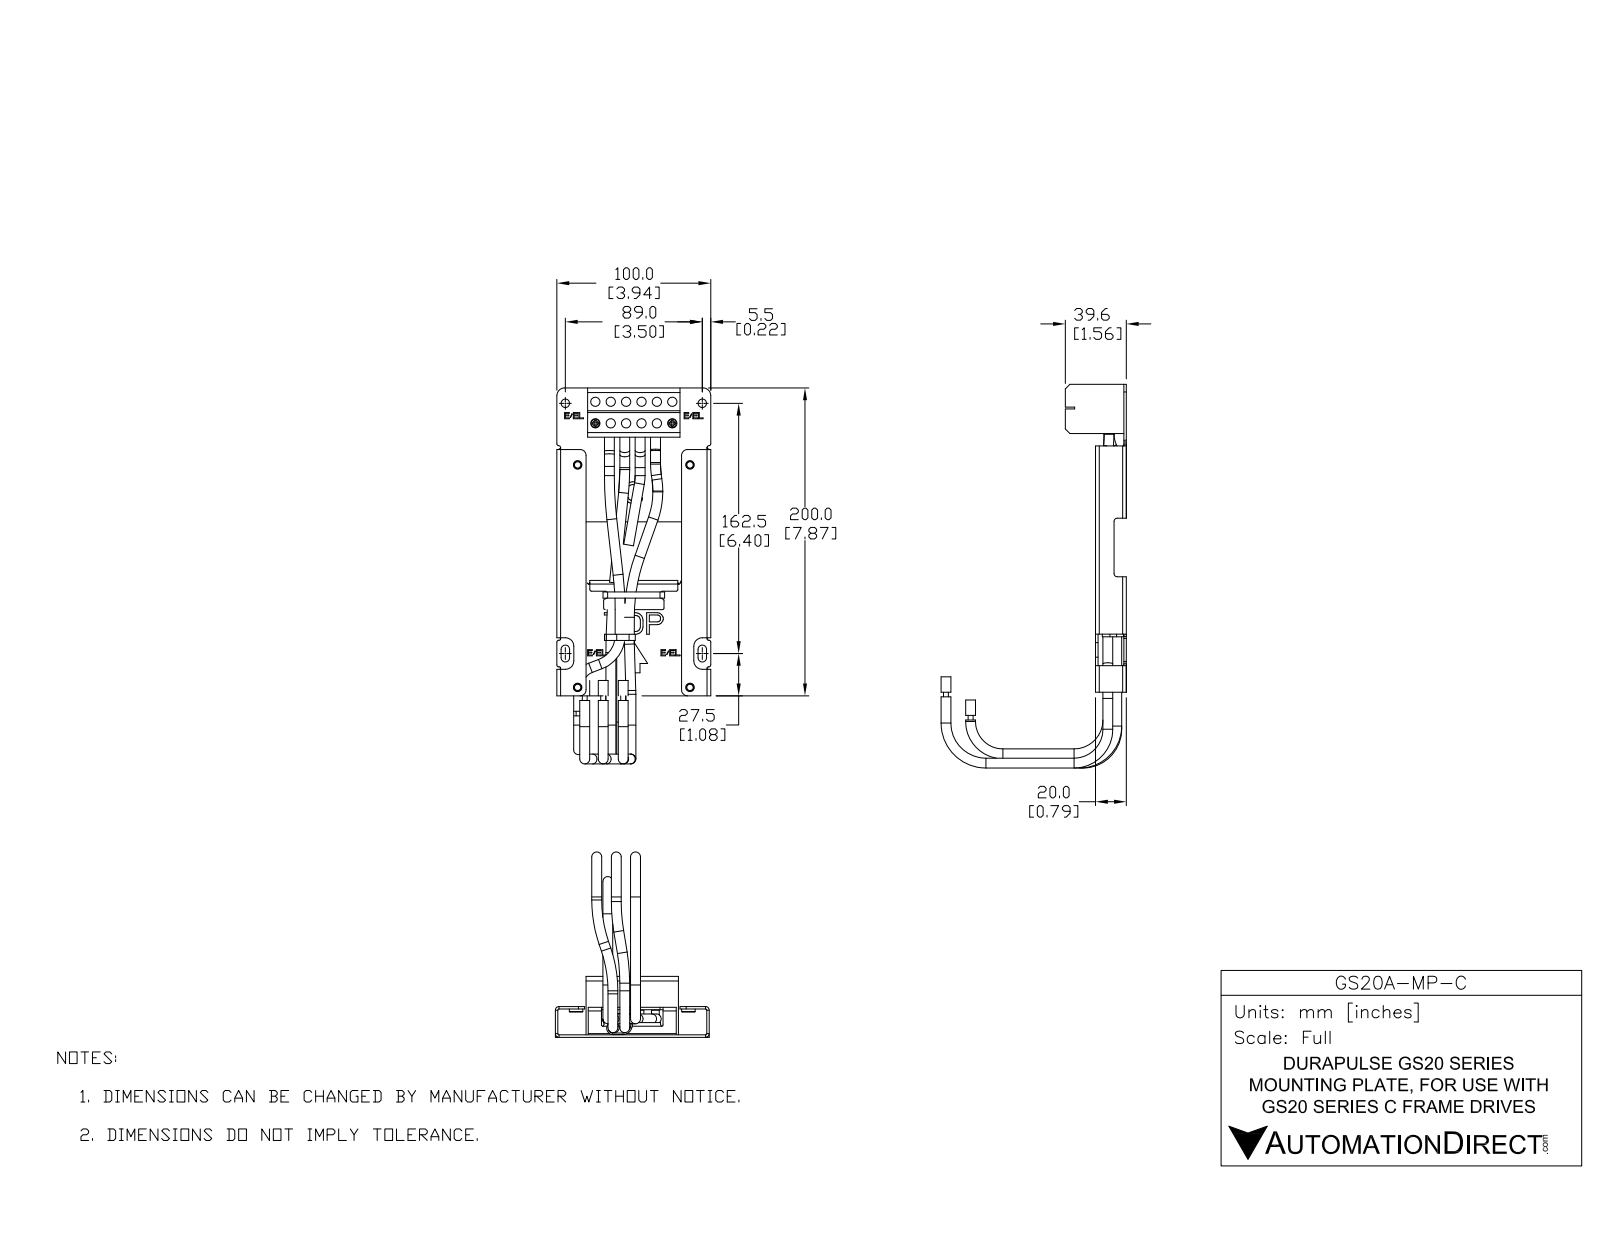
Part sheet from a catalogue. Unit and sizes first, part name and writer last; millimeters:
Units: millimetres
Overall size (bounding box): 244.2 × 117.4 × 100
Round holes (diameter × count): ⌀6 ×12, ⌀5.5 ×6, ⌀4.1 ×4, ⌀3 ×2
Round bosses / shafts (diameter × count): ⌀6.4 ×41, ⌀3.2 ×8, ⌀8.7 ×4, ⌀7.5 ×4, ⌀6.3 ×4, ⌀5.4 ×2
Partial cylindrical surfaces — rounded edges, fillets, slot ends (radius × count): R0.8 ×12, R1 ×10, R2 ×7, R1.2 ×6, R2.4 ×6, R3 ×6, R4 ×6, R0.5 ×4
Main face-to-face distances: 1.6, 18.4, 20, 16.8, 98.4, 80, 78.4, 32, 100, 96.8
Hole centre spacings: 10, 17.2, 20, 24.4, 14, 30, 33.1, 40
Volume: 142 900 mm³ · Surface area: 106 600 mm²
Bodies: 16 solids, 1118 faces (606 planar, 288 cylindrical, 224 other)
Part name (STEP PRODUCT): MKM-MAPC-PD-3D00 bfXT R2
STEP written by: SolidWorks 2017 (AUTOMOTIVE_DESIGN)
